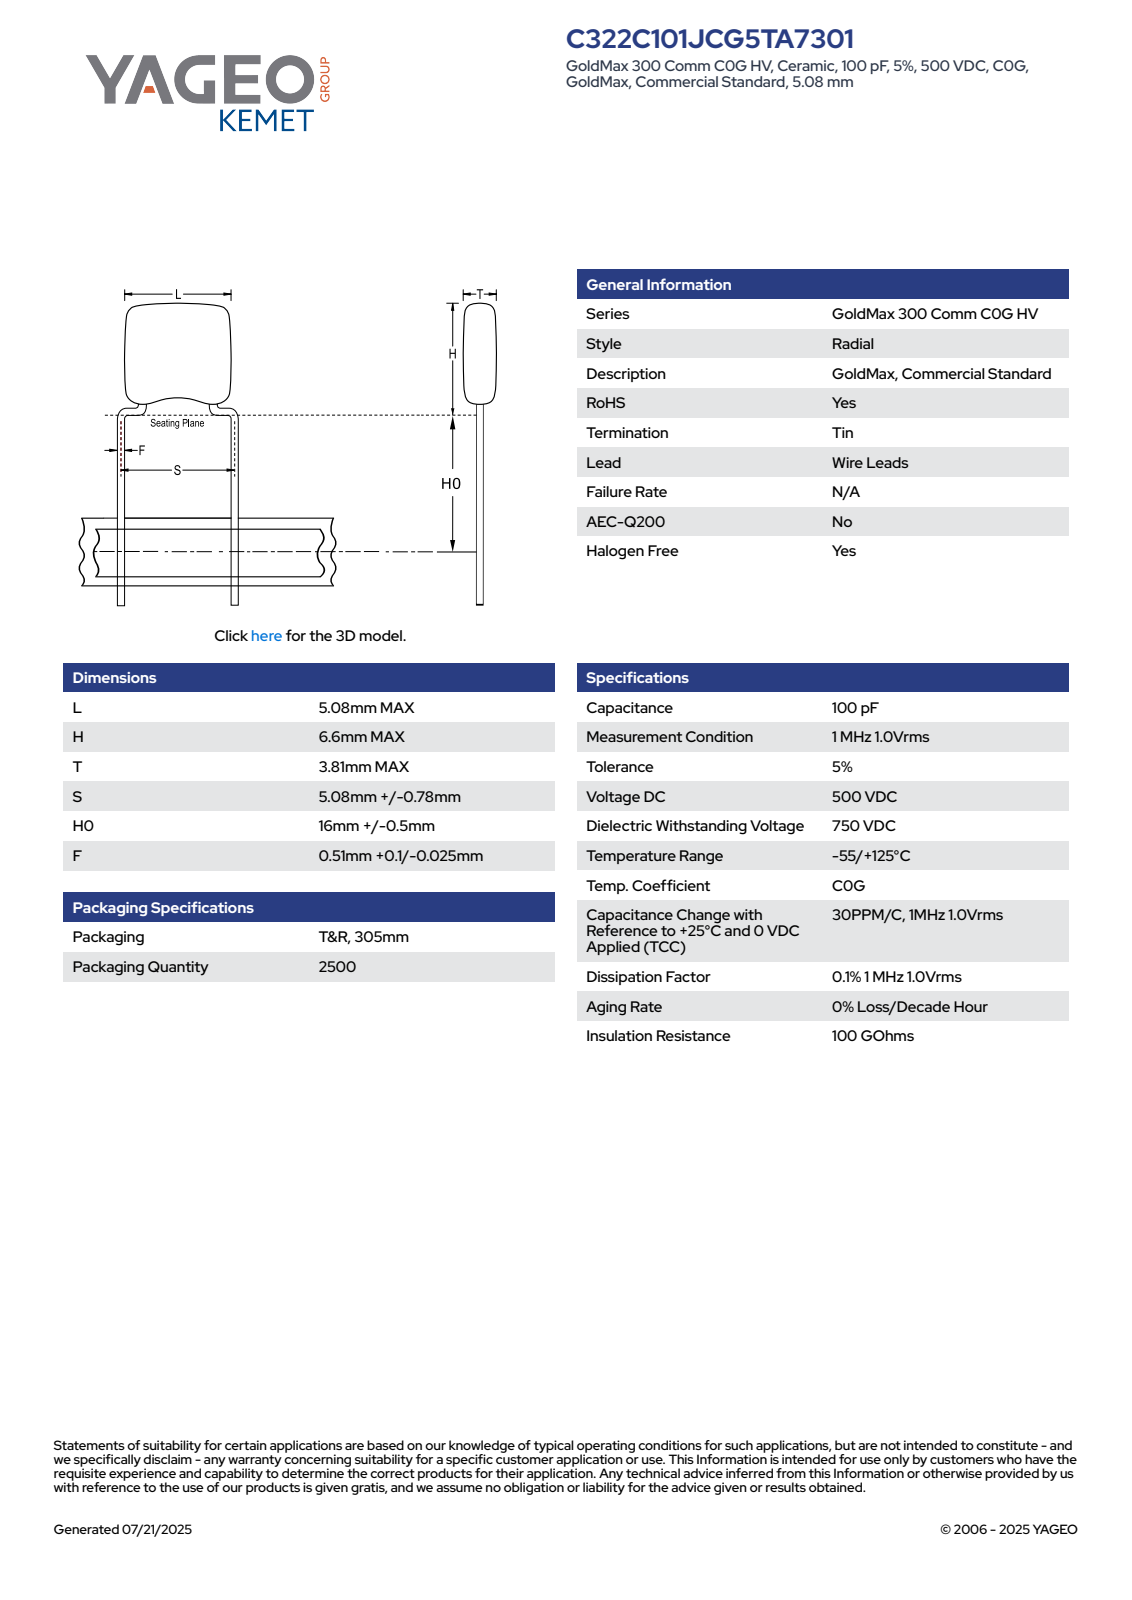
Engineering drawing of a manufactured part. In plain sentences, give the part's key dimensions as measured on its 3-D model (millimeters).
The part is named "CCR_SB_5.08X6.6_L5.08H6.6T3.81S5.08H016.5F0.51". Its 3-D file was written by "SolidWorks 2014 (AUTOMOTIVE_DESIGN)". It is 4 solids with 97 faces: 65 planar, 14 cylindrical and 18 other. Overall it measures 23.1 by 5.59 by 3.81 millimeters. Its volume is 92 cubic millimeters and its surface area 165 square millimeters. Round bosses or shafts: 2 of diameter 0.51. Partial cylindrical surfaces (rounded edges, fillets, slot ends): 10 of radius 1. The main face-to-face distances are 3.81, 5.08, 4.81, 0.43, 2.6, 2.21, 2.17, 2.64, 0.39, 0.35.
